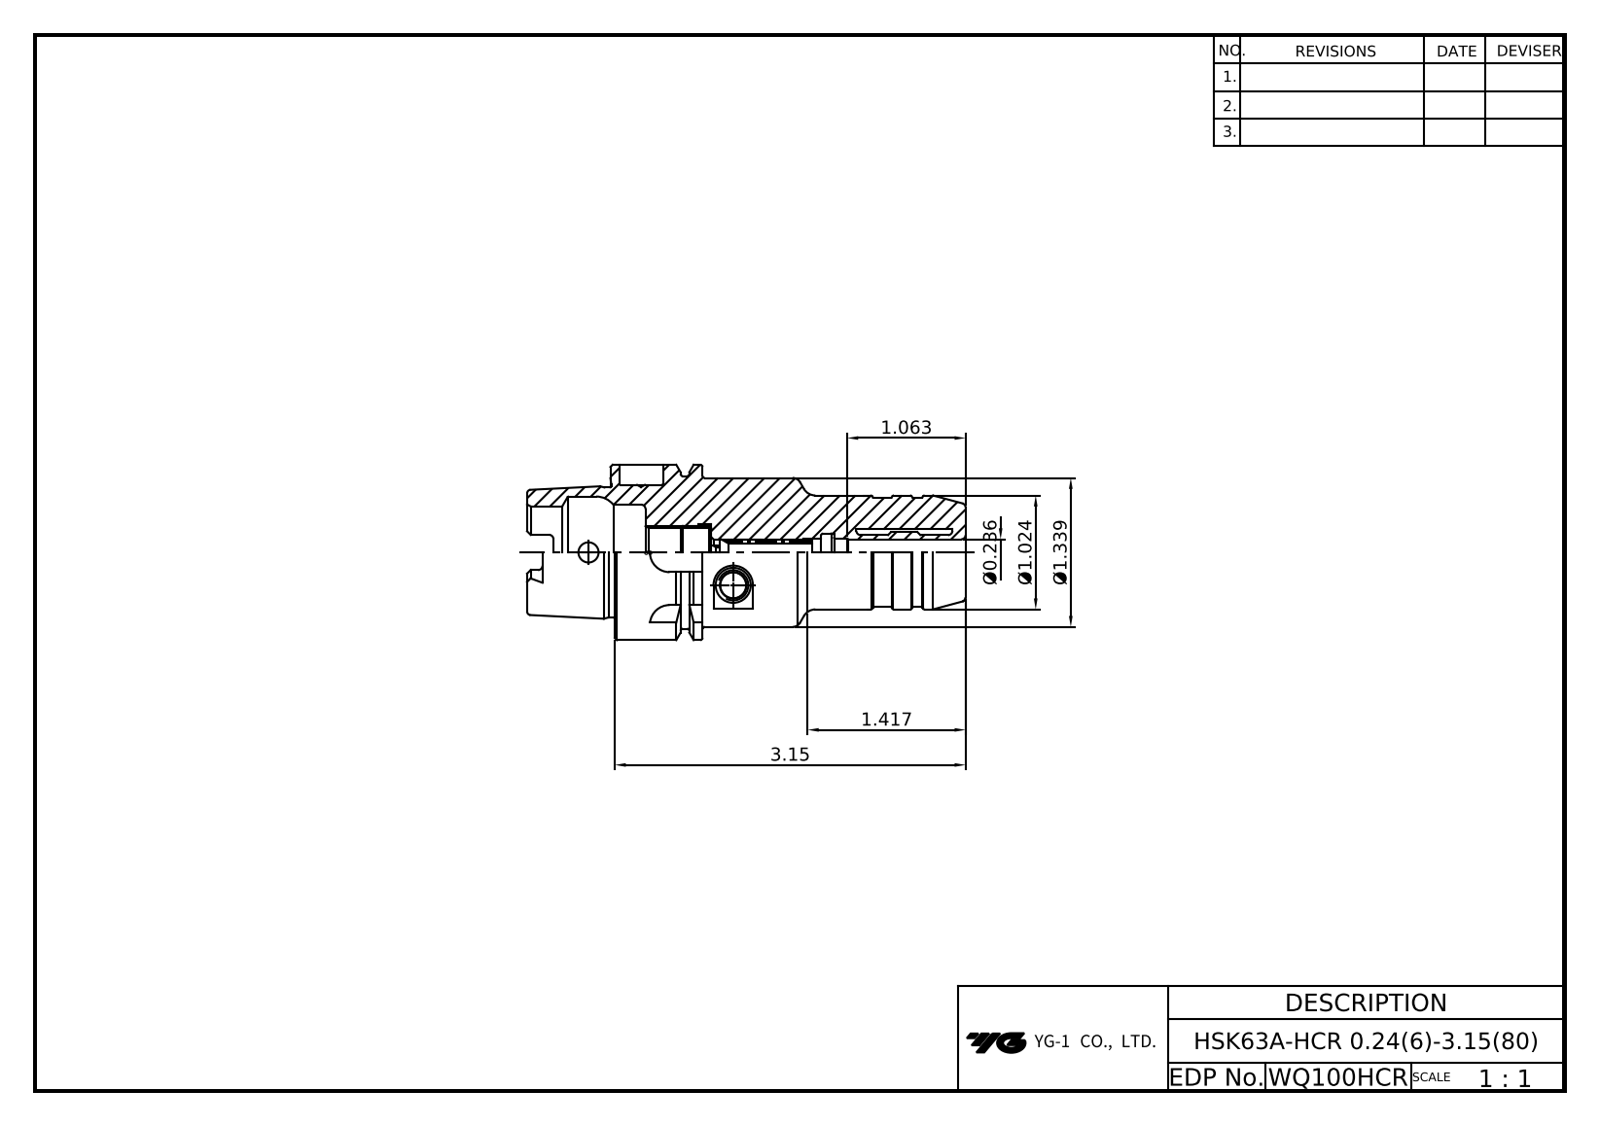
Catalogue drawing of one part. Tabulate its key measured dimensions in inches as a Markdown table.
| quantity | value |
| --- | --- |
| part name | HSK63A-HCR6-80 |
| STEP written by | PRO/ENGINEER BY PARAMETRIC TECHNOLOGY CORPORATION, 2012130 (CONFIG_CONTROL_DESIGN) |
| units | inches |
| bodies | 1 solid, 224 faces (57 planar, 65 cylindrical, 102 other) |
| overall size | 4.409 × 2.48 × 2.48 |
| volume | 8.031 in³ |
| surface area | 45.53 in² |
| round holes (diameter × count) | 0.236 × 1, 0.248 × 1, 0.252 × 1, 0.276 × 1, 0.295 × 1, 0.339 × 1, 0.394 × 1, 0.669 × 1, 0.709 × 1, 0.748 × 1, 1.339 × 1, 1.575 × 1 |
| round bosses / shafts (diameter × count) | 2.48 × 1, 2.165 × 1, 1.969 × 1, 1.891 × 1, 1.024 × 1, 0.984 × 1 |
| partial cylindrical surfaces (radius × count) | 0.059 × 6, 0.113 × 4, 0.315 × 4 |
| main face-to-face distances | 1.024, 0.394, 0.63, 1.26, 1.654, 0.241, 0.389, 2.283, 2.087, 4.409 |
